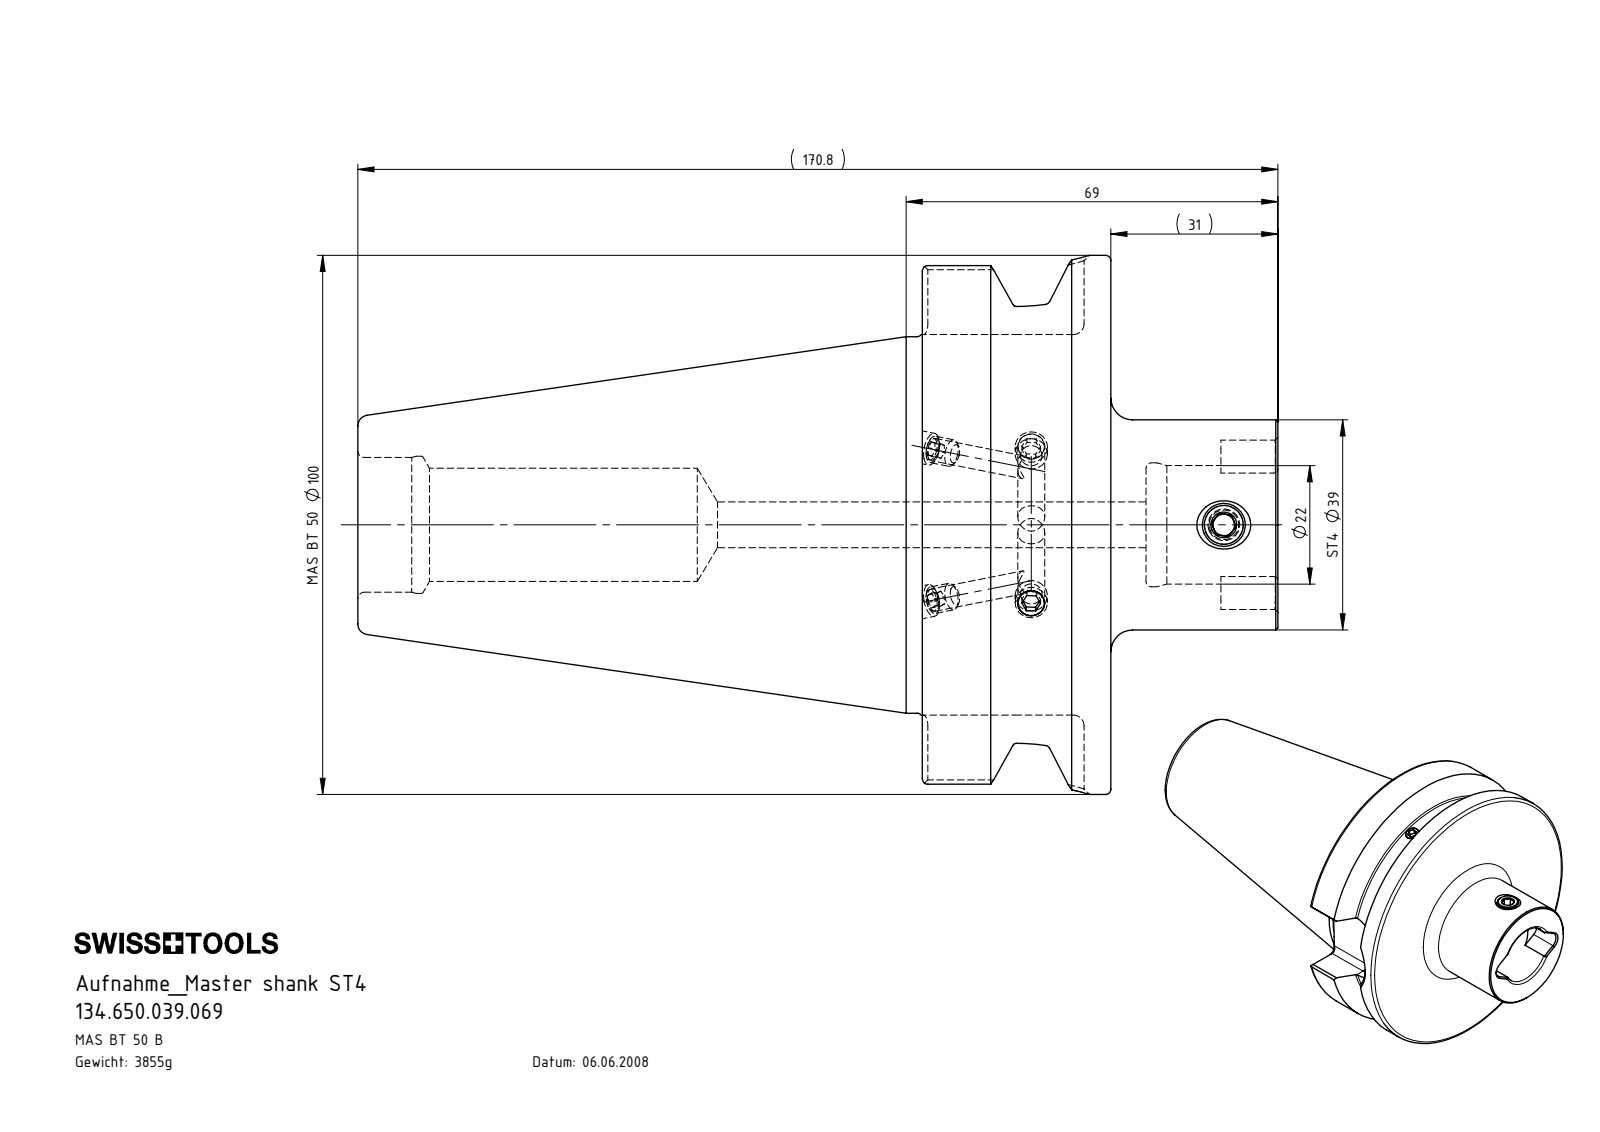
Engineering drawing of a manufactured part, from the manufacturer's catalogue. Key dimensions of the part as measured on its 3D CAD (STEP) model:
Part name (STEP PRODUCT): ISO 4026 - M6 x 5; ST4-ER1.001.011_A; BB5-ST4.K01.069_A_mit Bundkhlung; BB5-ST4.K01.069
STEP written by: SolidWorks 2015 (CONFIG_CONTROL_DESIGN)
Units: millimetres
Bodies: 3 solids, 168 faces (45 planar, 53 cylindrical, 70 other)
Overall size (bounding box): 170.8 × 100 × 100
Volume: 490 602 mm³ · Surface area: 58 464 mm²
Round holes (diameter × count): ⌀6 ×2, ⌀5 ×1, ⌀7.25 ×1, ⌀8.5 ×1, ⌀21 ×1, ⌀22 ×1, ⌀23 ×1, ⌀25 ×1, ⌀25.45 ×1
Round bosses / shafts (diameter × count): ⌀100 ×1, ⌀85 ×1, ⌀69.85 ×1, ⌀39 ×1, ⌀8 ×1, ⌀6 ×1
Partial cylindrical surfaces — rounded edges, fillets, slot ends (radius × count): R2 ×8, R3.2 ×2, R12.85 ×1
Main face-to-face distances: 35, 66, 31, 70.6, 104.8, 139.8, 170.8, 25.7, 146.3, 41.5
